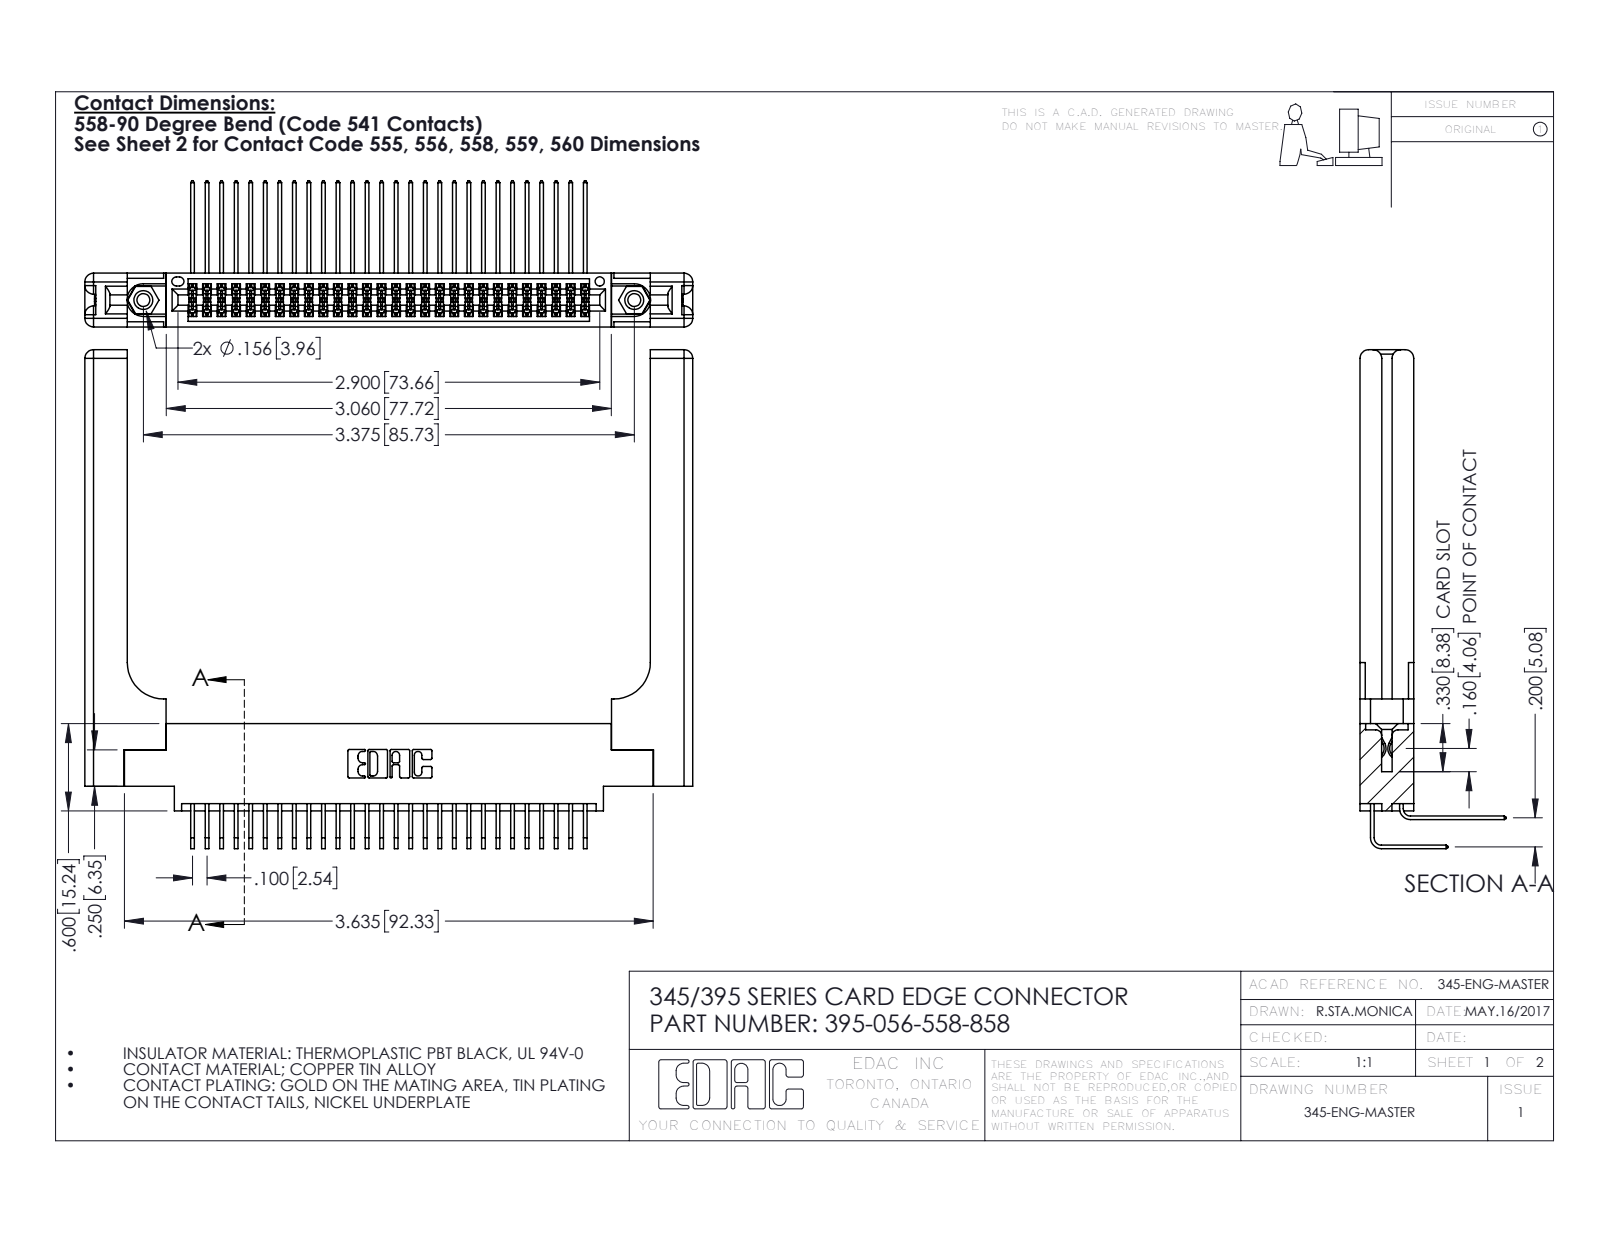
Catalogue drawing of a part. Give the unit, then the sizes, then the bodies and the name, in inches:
Units: inches
Overall size (bounding box): 4.179 × 3.429 × 1.005
Round holes (diameter × count): ⌀0.089 ×2, ⌀0.125 ×2, ⌀0.156 ×2, ⌀0.064 ×1
Round bosses / shafts (diameter × count): ⌀0.155 ×2
Partial cylindrical surfaces — rounded edges, fillets, slot ends (radius × count): R0.006 ×112, R0.01 ×22, R0.06 ×16, R0.007 ×6, R0.031 ×6, R0.026 ×3, R0.014 ×2, R0.019 ×2
Main face-to-face distances: 0.37, 0.072, 0.298, 0.2, 0.098, 0.272, 0.025, 0.225, 0.148, 0.15
Hole centre spacings: 0.27, 3.14, 3.375
Volume: 1.151 in³ · Surface area: 33.81 in²
Bodies: 61 solids, 3298 faces (2192 planar, 1046 cylindrical, 60 other)
Part name (STEP PRODUCT): 345-292-001_558 559 Tail - 1; 345-250-001_345-250-001-102; 345-292-001_558 Tail - 2; 345-220-058_345-220-058 (+2 more)
STEP written by: SolidWorks 2016 (CONFIG_CONTROL_DESIGN)
